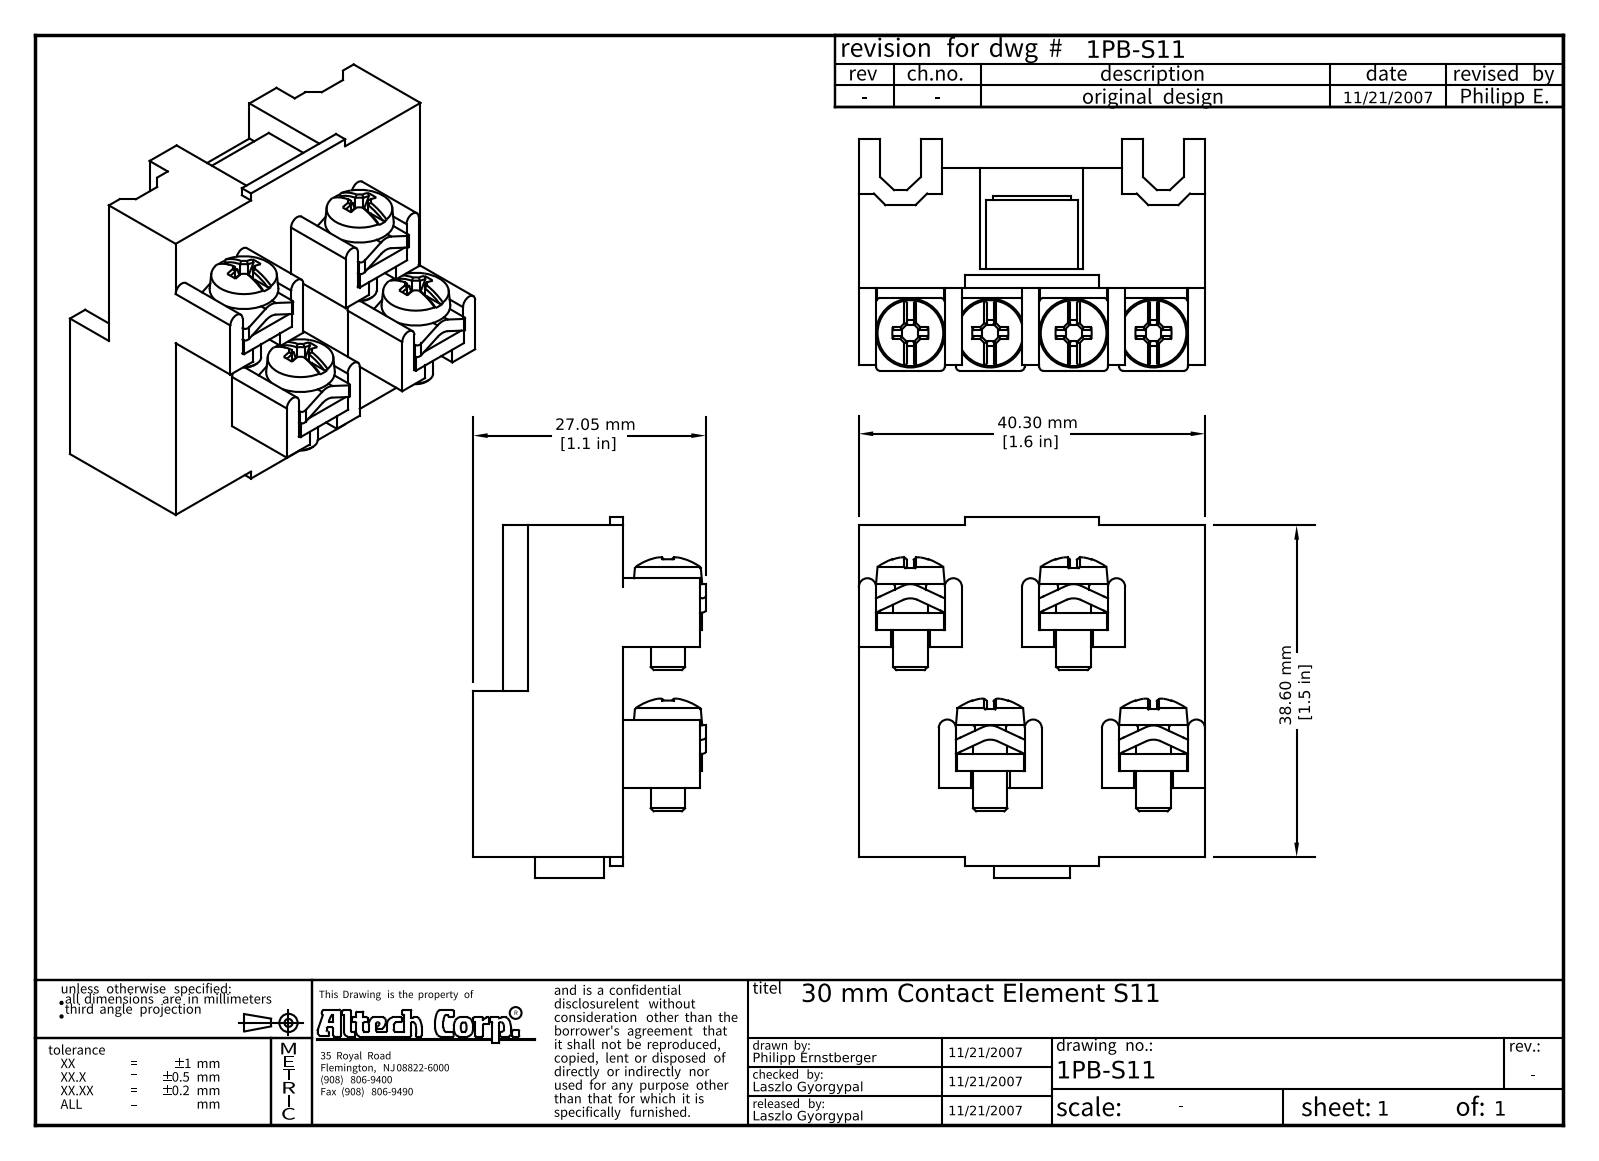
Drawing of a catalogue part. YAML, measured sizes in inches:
part_name: "S11; casing; pin; DIN 7985 (H) M4x10-H (+1 more)"
step_written_by: "Autodesk Inventor 2008 (AUTOMOTIVE_DESIGN)"
units: inches
bodies: {solids: 10, faces: 374, planar: 227, cylindrical: 56, other: 91}
overall_size: [1.654, 1.587, 1.065]
volume: 1.416
surface_area: 19.71
round_holes:
  - {diameter: 0.157, count: 4}
round_bosses_or_shafts:
  - {diameter: 0.144, count: 4}
partial_cylinders:
  - {radius: 0.02, count: 16}
  - {radius: 0.039, count: 8}
  - {radius: 0.079, count: 8}
  - {radius: 0.089, count: 4}
face_to_face_distances: [0.465, 0.087, 0.551, 1.587, 0.967, 0.62, 0.648, 0.354, 0.557, 0.315]
hole_center_spacings: [0.366, 0.748, 0.382, 1.114]
